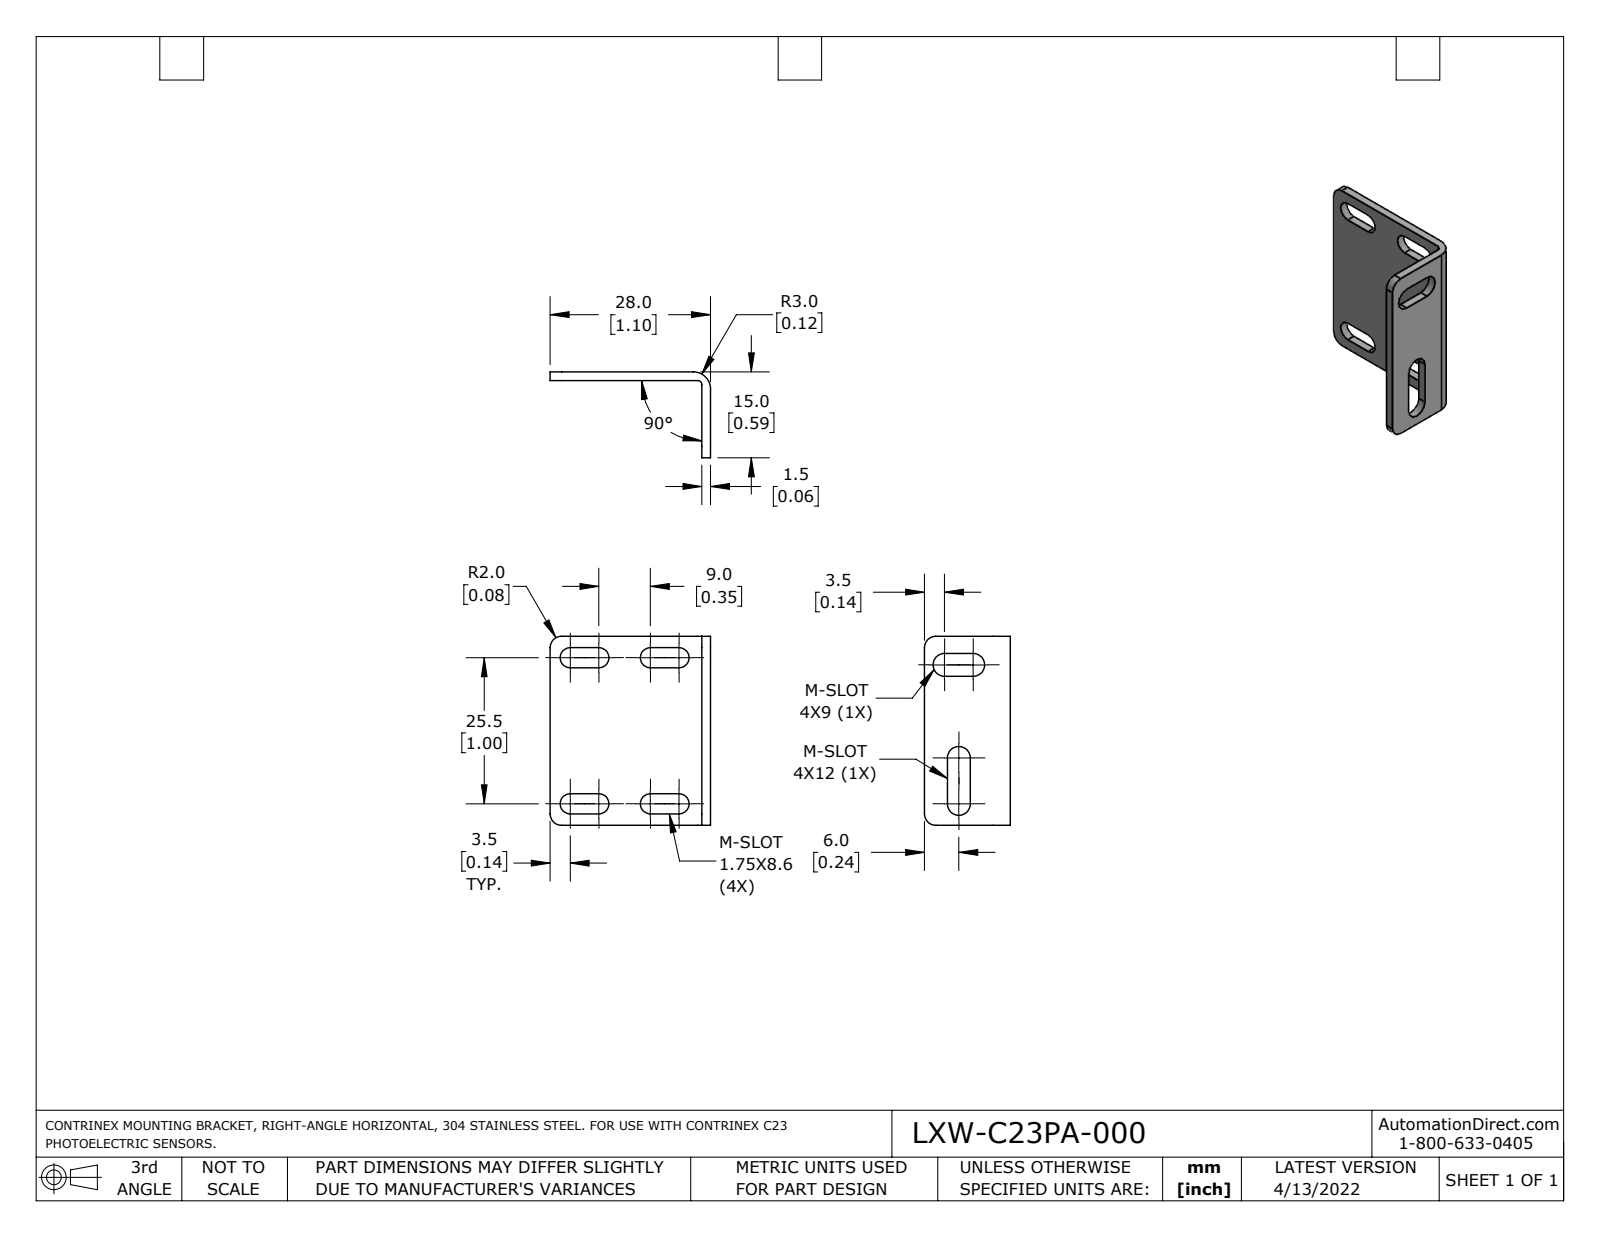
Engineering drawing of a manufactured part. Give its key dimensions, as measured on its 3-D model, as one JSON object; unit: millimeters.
{"part_name": "LXW-C23PA-000", "step_written_by": "PARTsolutions (AUTOMOTIVE_DESIGN)", "units": "millimeters", "bodies": {"solids": 1, "faces": 38, "planar": 20, "cylindrical": 18, "other": 0}, "overall_size": [33, 28, 15], "volume_mm3": 1711, "surface_area_mm2": 2725, "partial_cylinders_radius": [[1.75, 8], [2, 8], [0.75, 1], [3, 1]], "face_to_face_distances": [1.5, 33, 28, 26.5, 15, 13.5, 5.5, 4, 2, 27.5]}
